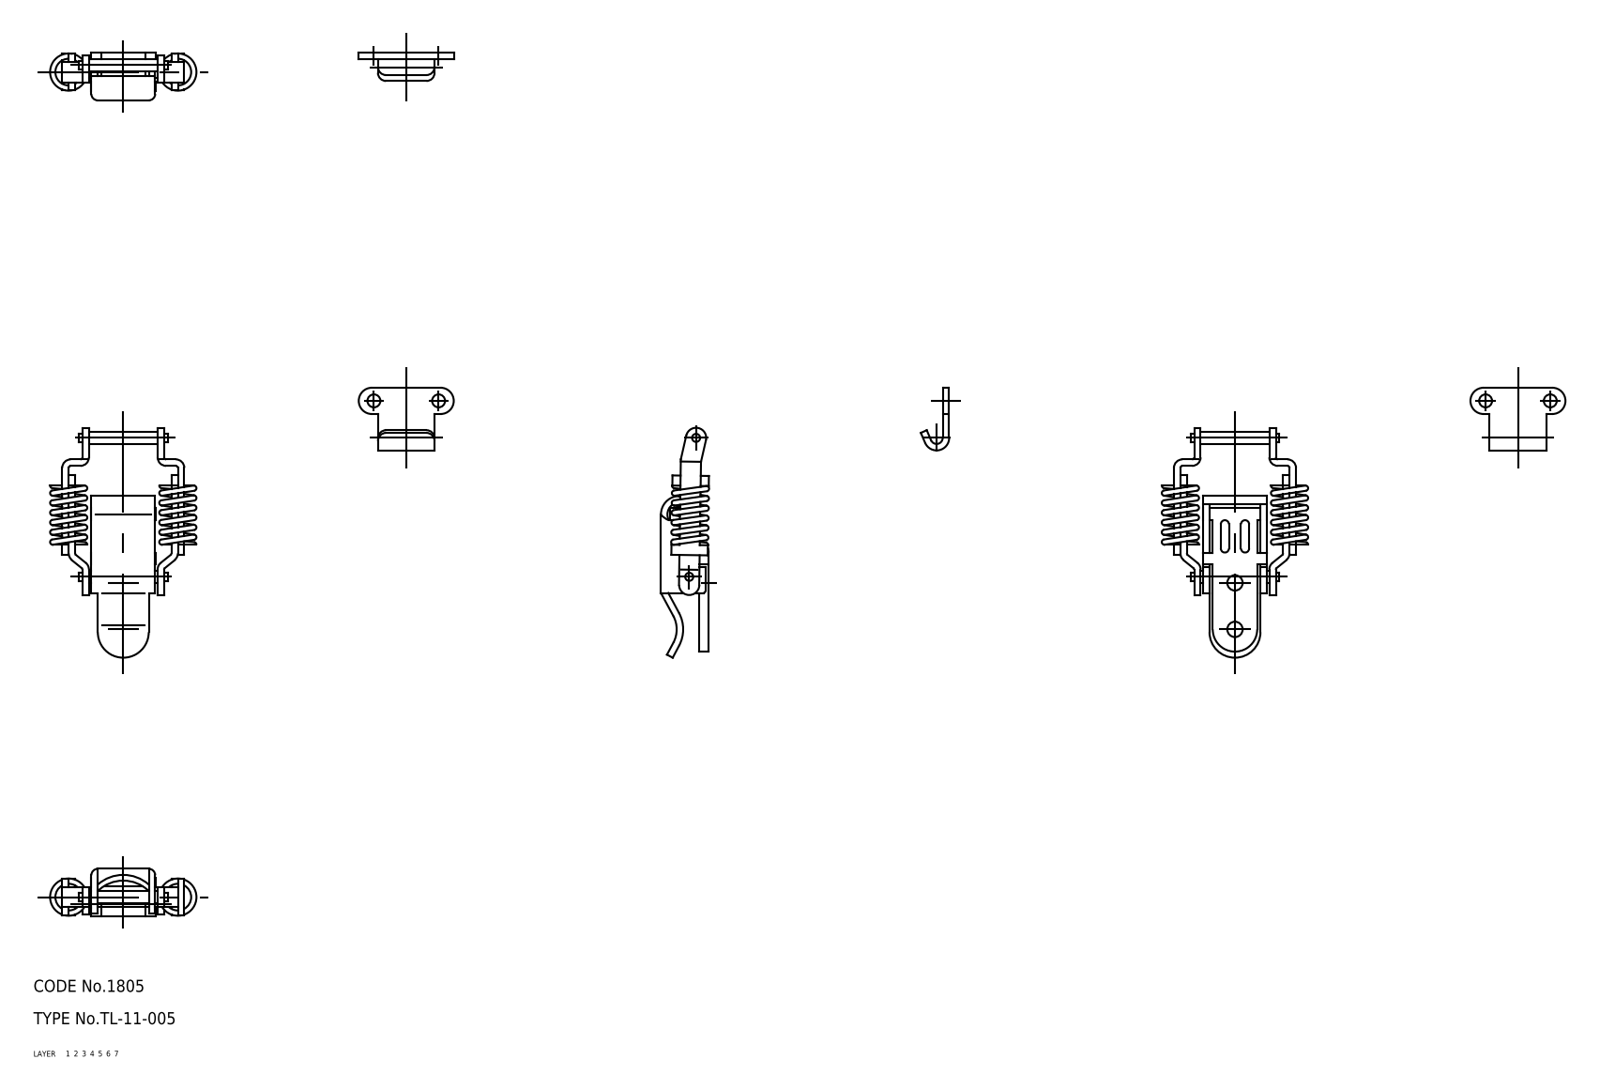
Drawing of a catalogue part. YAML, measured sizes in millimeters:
part_name: "arm_C_mr; arm_C; arm_B; arm_A (+6 more)"
step_written_by: "CADfix (AUTOMOTIVE_DESIGN)"
units: millimeters
bodies: {solids: 11, faces: 281, planar: 0, cylindrical: 0, other: 281}
overall_size: [66.75, 37, 11.8]
volume: 4775
surface_area: 7847
